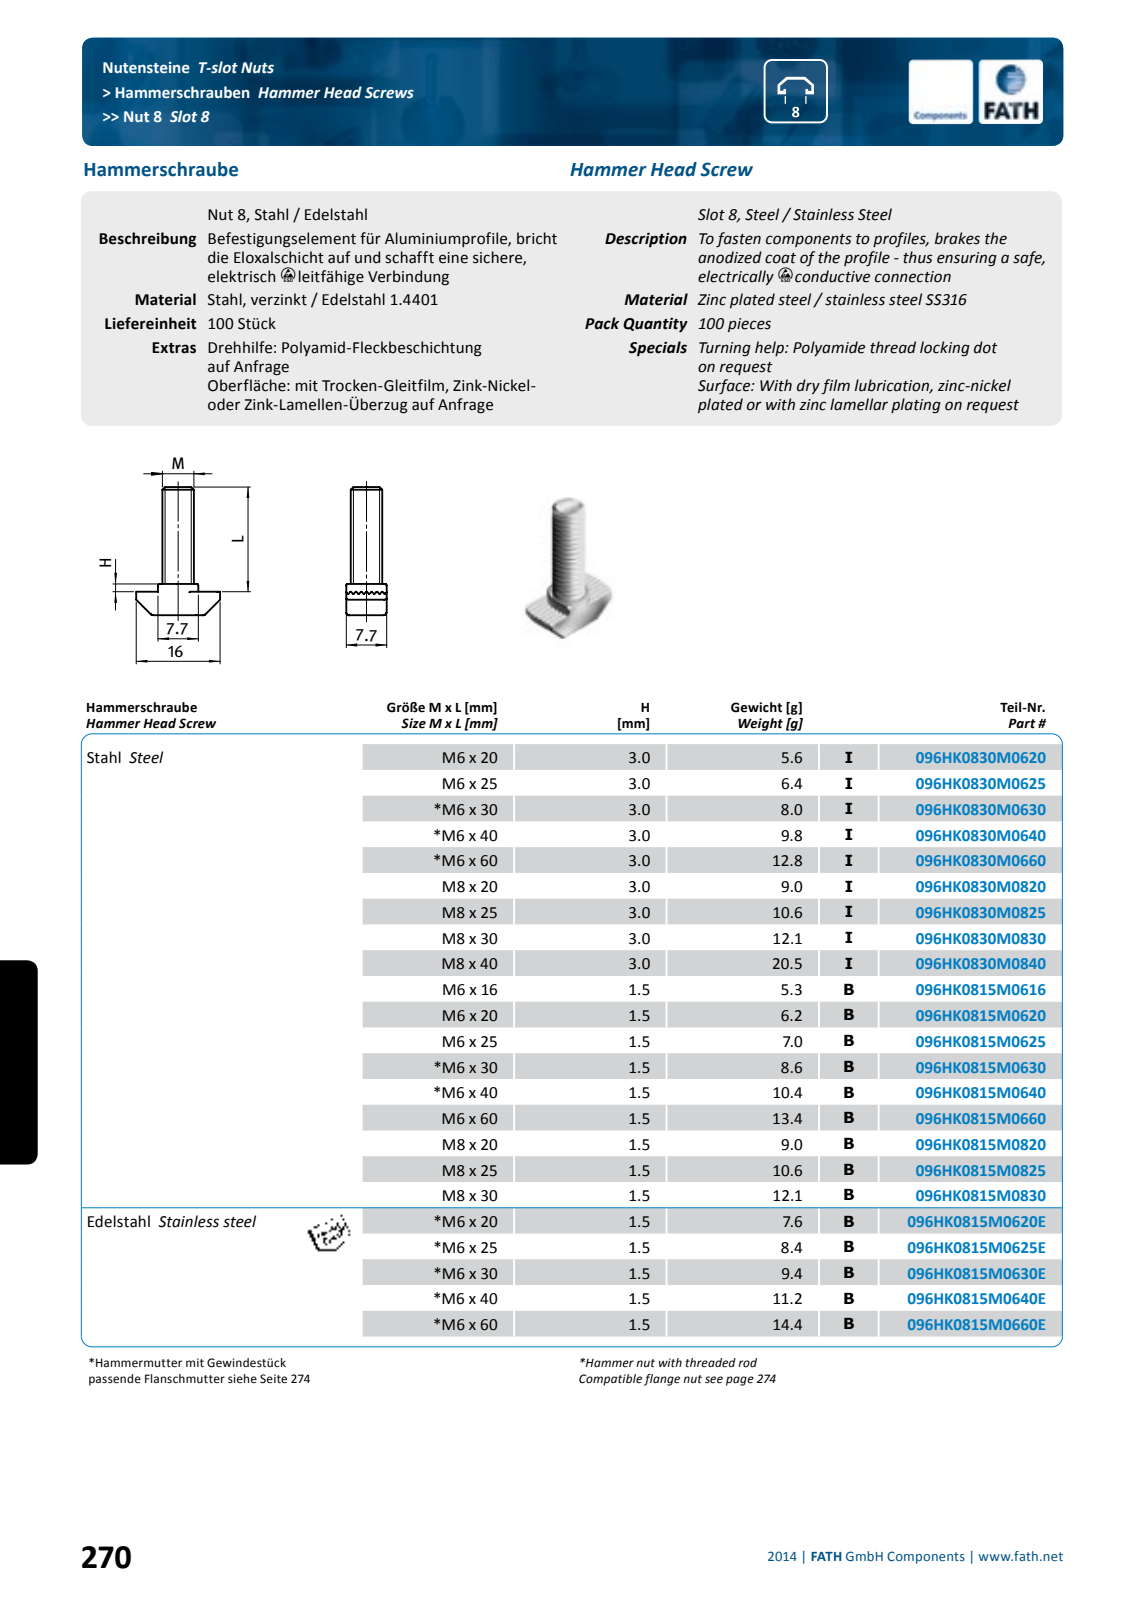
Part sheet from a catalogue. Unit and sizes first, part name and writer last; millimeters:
Units: millimetres
Overall size (bounding box): 44.5 × 16 × 8
Round bosses / shafts (diameter × count): ⌀6 ×1
Partial cylindrical surfaces — rounded edges, fillets, slot ends (radius × count): R0.1 ×8, R1 ×6, R3.85 ×2, R8 ×1
Main face-to-face distances: 8, 0.71, 2.12, 1.41, 6, 2.83, 3.53, 4.24, 44.5, 38.5
Volume: 1 646 mm³ · Surface area: 1 191 mm²
Bodies: 1 solid, 99 faces (45 planar, 50 cylindrical, 4 other)
Part name (STEP PRODUCT): fath_096hk0815m0640
STEP written by: Spatial InterOp 3D (automotive_design)
